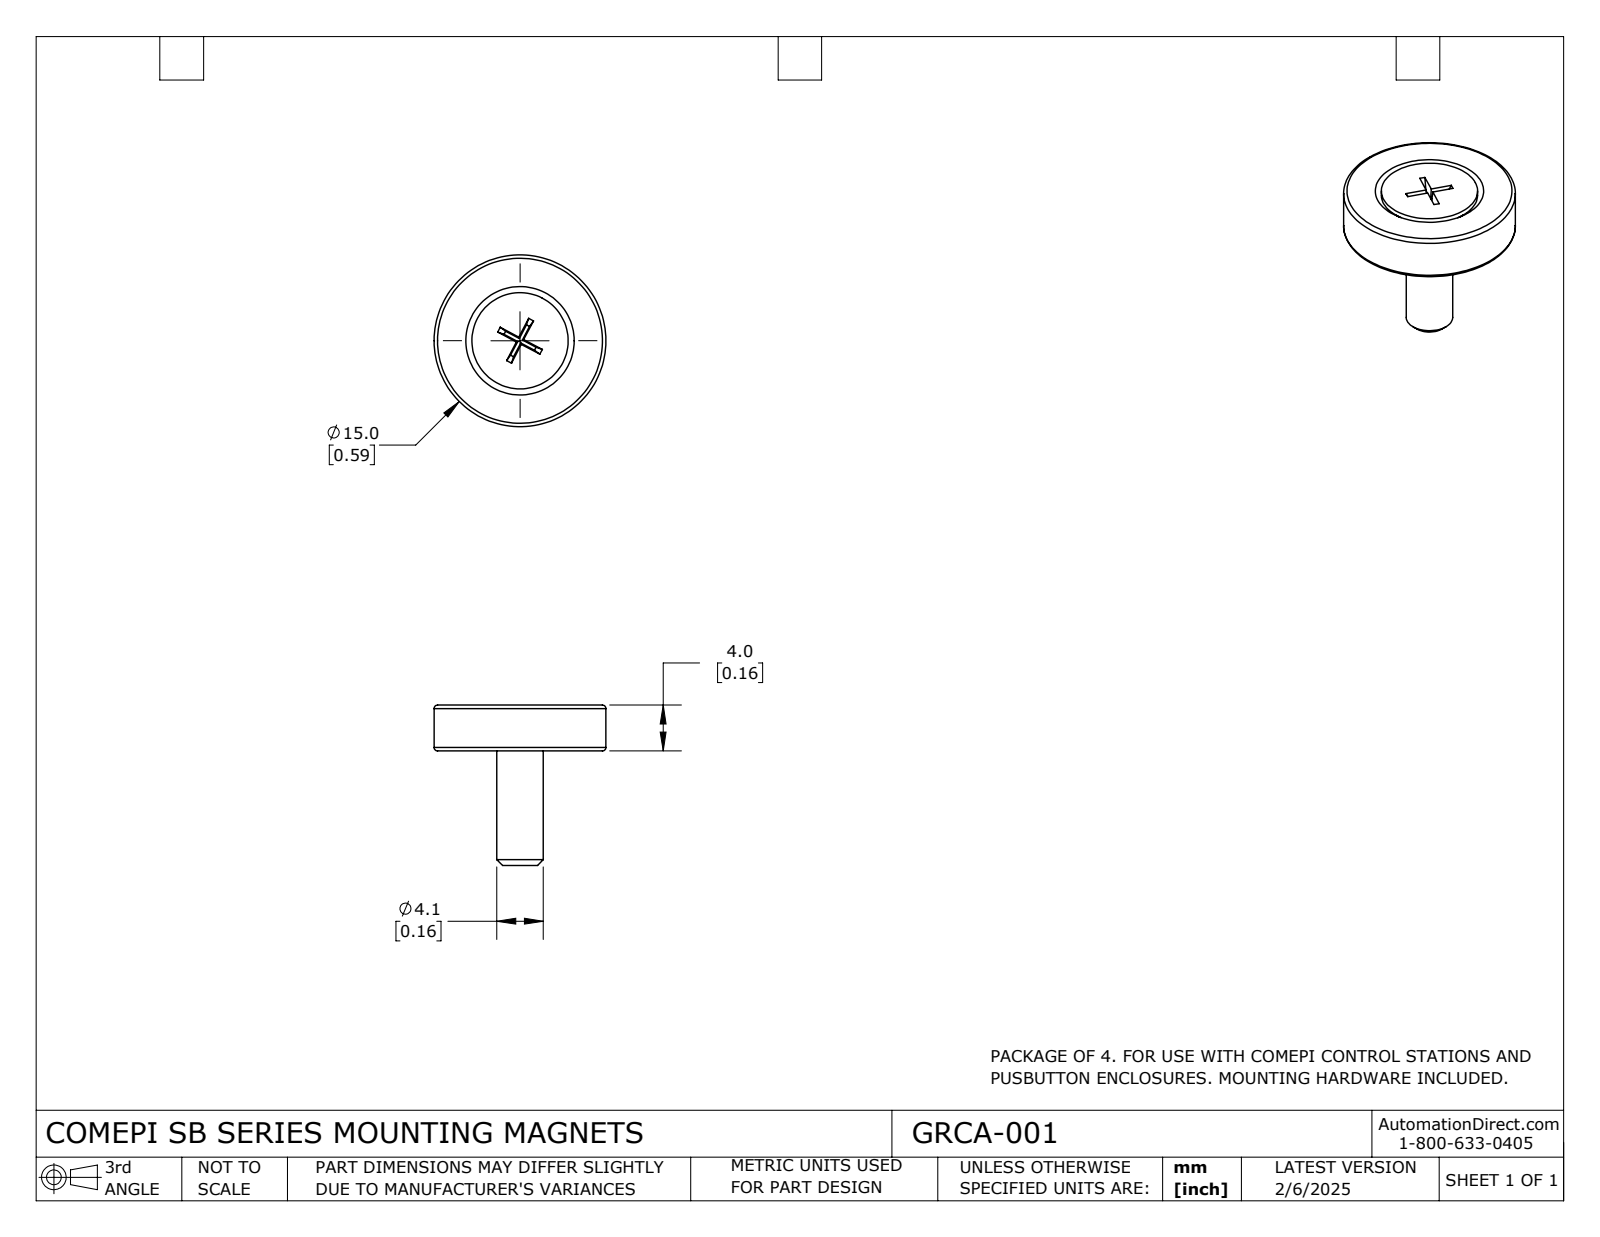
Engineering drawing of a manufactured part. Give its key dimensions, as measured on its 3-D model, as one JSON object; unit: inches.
{"part_name": "GRCA-001", "step_written_by": "SolidWorks 2024 (CONFIG_CONTROL_DESIGN)", "units": "inches", "bodies": {"solids": 2, "faces": 35, "planar": 17, "cylindrical": 8, "other": 10}, "overall_size": [0.591, 0.591, 0.551], "volume_in3": 0.05, "surface_area_in2": 1.296, "round_holes": [[0.177, 1]], "round_bosses_or_shafts": [[0.591, 1], [0.331, 1], [0.16, 1]], "face_to_face_distances": [0.157, 0.551, 0.394, 0.039, 0.118, 0.512]}
